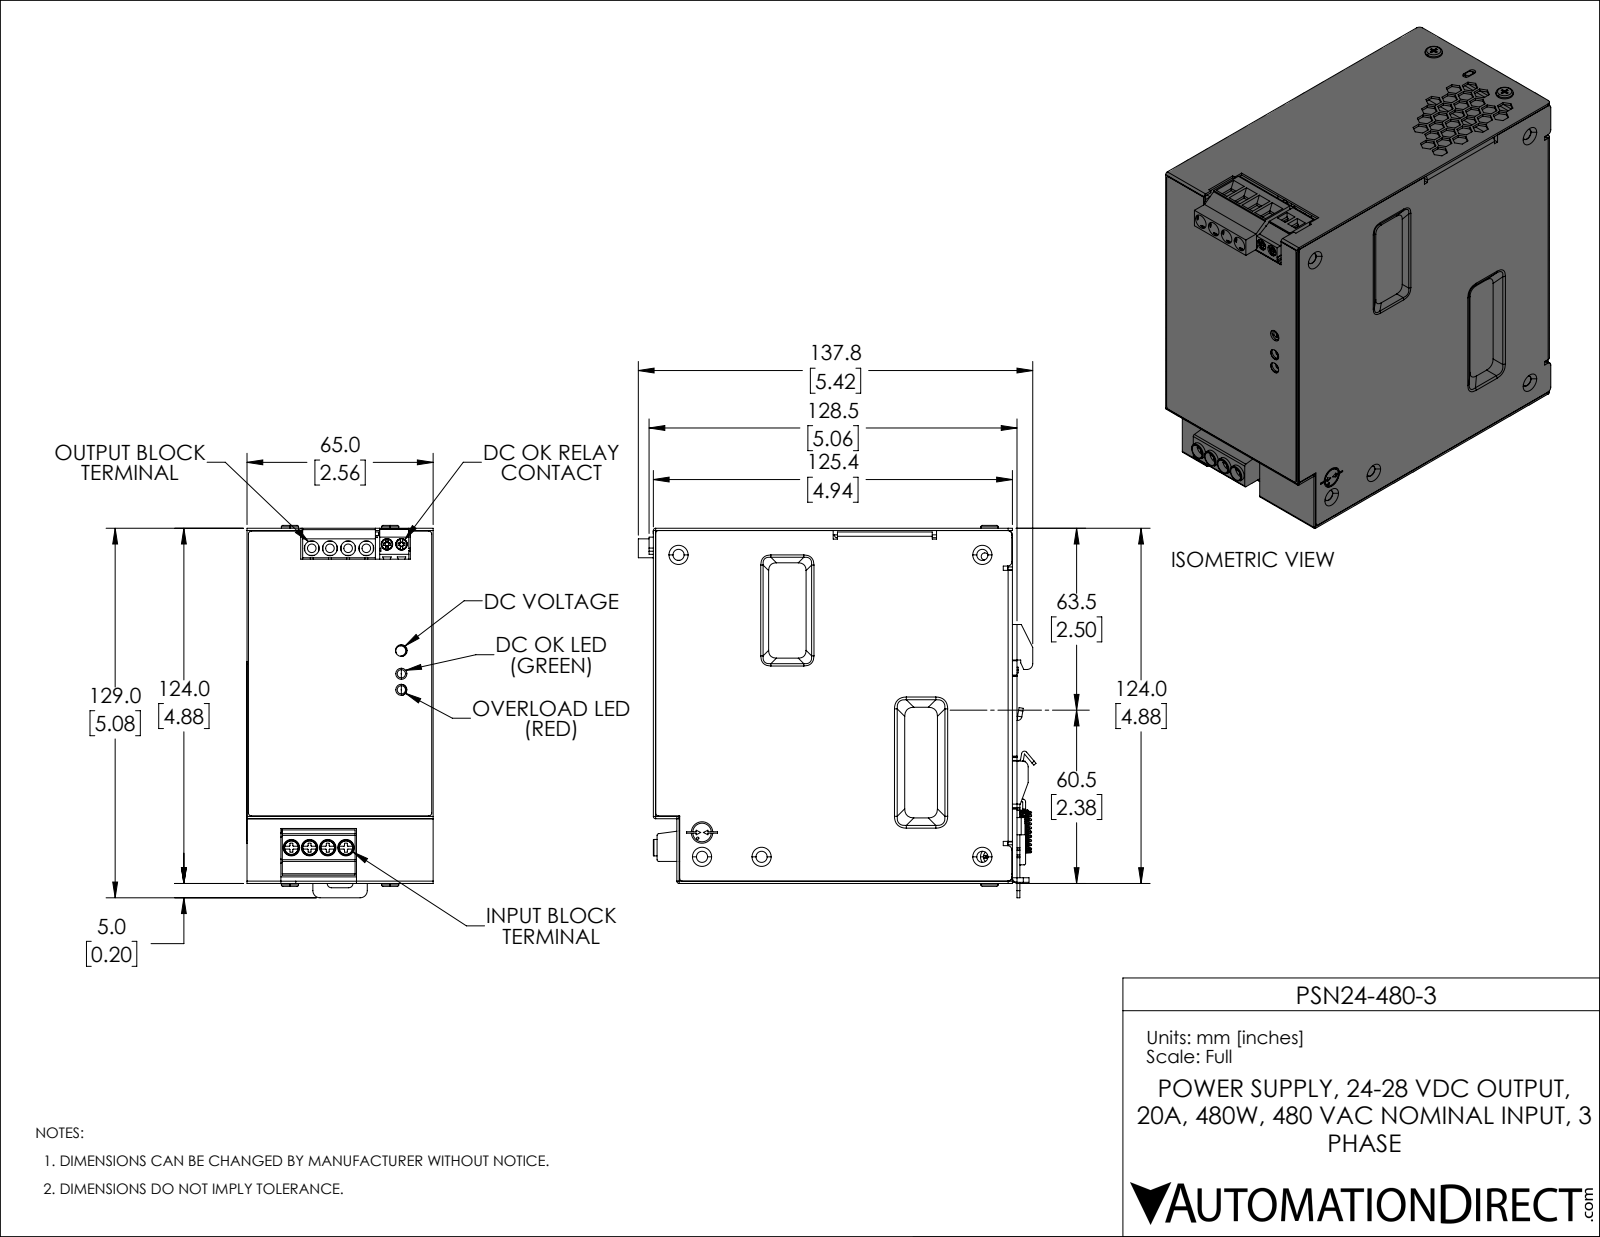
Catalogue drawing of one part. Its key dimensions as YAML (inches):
part_name: "PSN24-480-3"
step_written_by: "SolidWorks 2019 (AUTOMOTIVE_DESIGN)"
units: inches
bodies: {solids: 21, faces: 2601, planar: 1942, cylindrical: 526, other: 133}
overall_size: [5.468, 5.118, 2.561]
volume: 6.013
surface_area: 261.3
round_holes:
  - {diameter: 0.154, count: 16}
  - {diameter: 0.098, count: 7}
  - {diameter: 0.157, count: 5}
  - {diameter: 0.118, count: 4}
  - {diameter: 0.138, count: 4}
  - {diameter: 0.193, count: 4}
  - {diameter: 0.205, count: 4}
  - {diameter: 0.22, count: 3}
  - {diameter: 0.039, count: 2}
  - {diameter: 0.031, count: 1}
  - {diameter: 0.146, count: 1}
  - {diameter: 0.295, count: 1}
round_bosses_or_shafts:
  - {diameter: 0.157, count: 7}
  - {diameter: 0.226, count: 4}
  - {diameter: 0.185, count: 4}
  - {diameter: 0.236, count: 2}
  - {diameter: 0.154, count: 2}
  - {diameter: 0.118, count: 2}
  - {diameter: 0.114, count: 2}
  - {diameter: 0.079, count: 2}
partial_cylinders:
  - {radius: 0.01, count: 60}
  - {radius: 0.02, count: 45}
  - {radius: 0.039, count: 39}
  - {radius: 0.059, count: 33}
  - {radius: 0.012, count: 20}
  - {radius: 0.008, count: 17}
  - {radius: 0.004, count: 16}
  - {radius: 0.197, count: 16}
face_to_face_distances: [0.059, 2.5, 0.031, 2.441, 4.85, 2.559, 4.937, 4.819, 4.878, 4.882]
hole_center_spacings: [0.25, 0.787, 3.075, 3.213, 0.295, 0.5, 2.886, 3.075]
